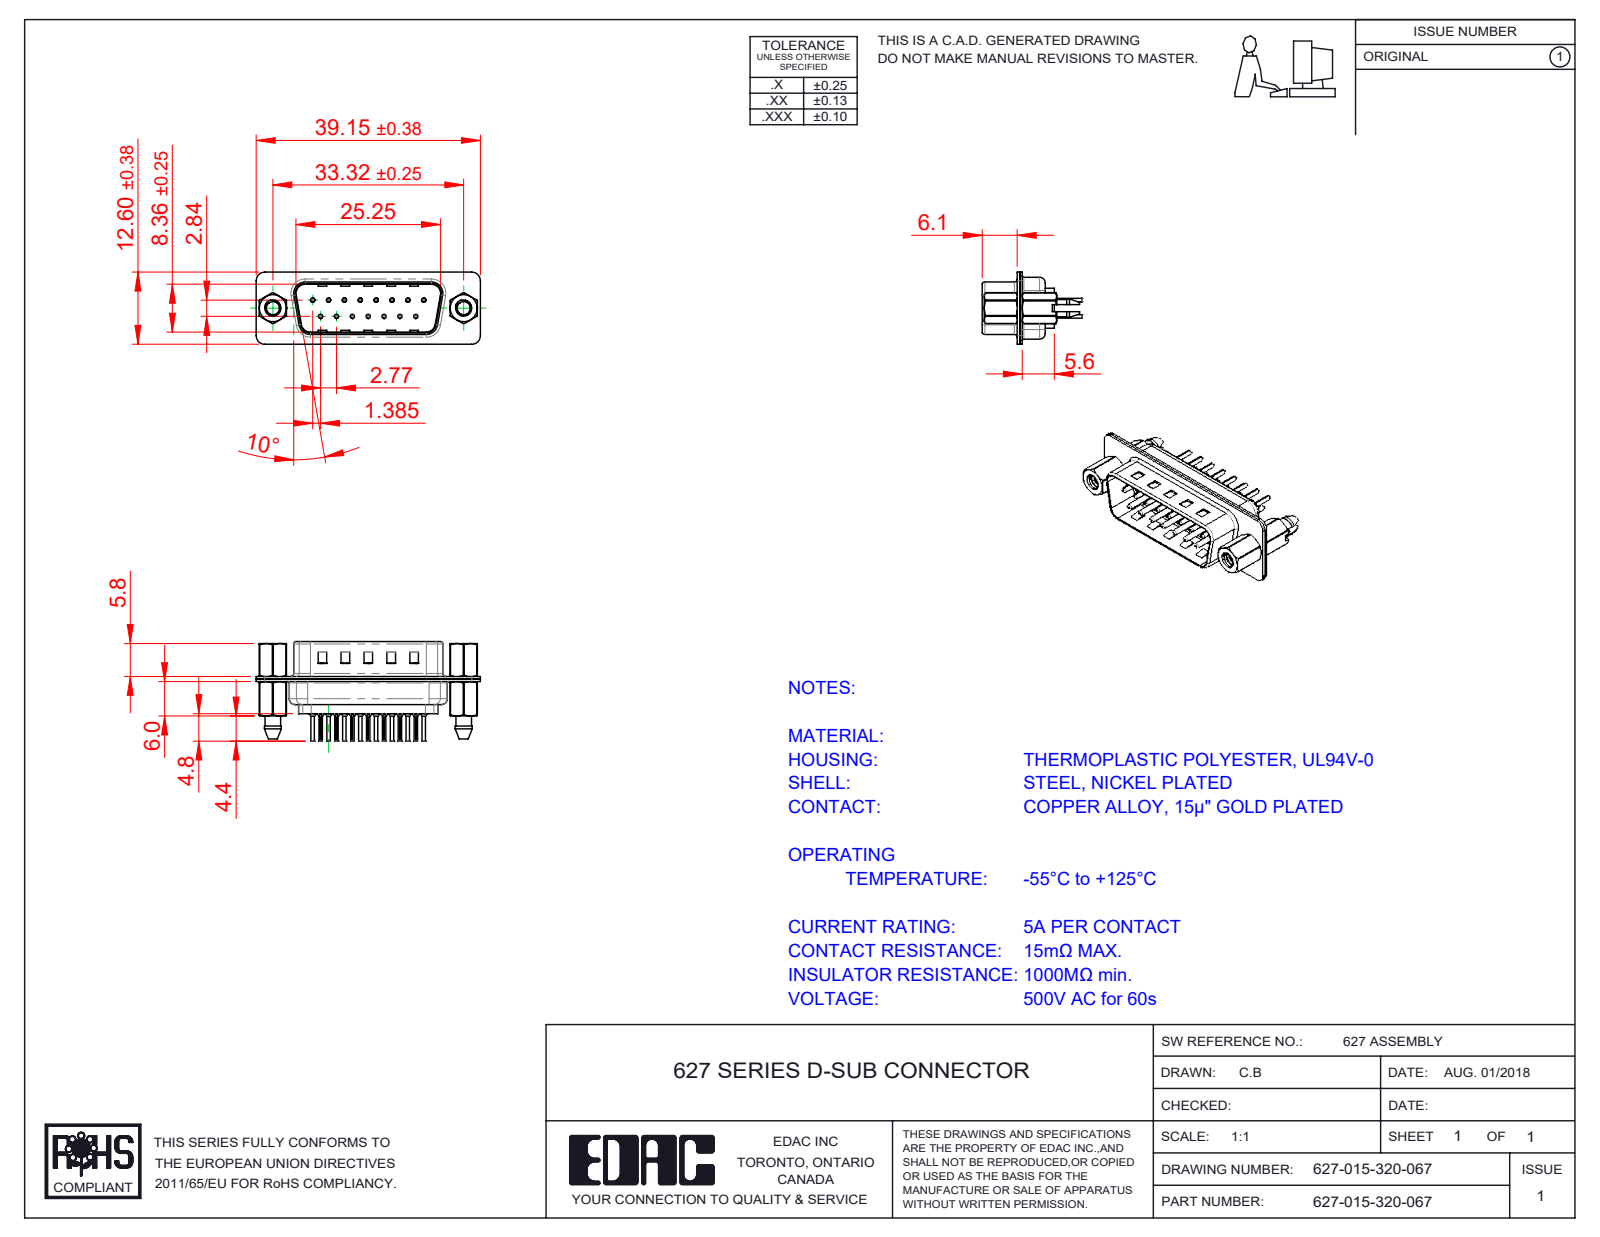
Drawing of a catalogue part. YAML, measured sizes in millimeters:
part_name: "627-015-320-067; 627 4-40 Hex Standoff; 627 Shell Front_15 Contacts; 627 Contact Row 1_20L (+4 more)"
step_written_by: "SolidWorks 2020 (CONFIG_CONTROL_DESIGN)"
units: millimeters
bodies: {solids: 22, faces: 2010, planar: 553, cylindrical: 792, other: 665}
overall_size: [39.15, 17.3, 12.6]
volume: 2158
surface_area: 6166
round_holes:
  - {diameter: 0.2, count: 15}
  - {diameter: 0.35, count: 15}
  - {diameter: 1.1, count: 15}
  - {diameter: 1.6, count: 15}
  - {diameter: 2.26, count: 2}
  - {diameter: 2.29, count: 2}
  - {diameter: 4, count: 2}
  - {diameter: 4.8, count: 2}
round_bosses_or_shafts:
  - {diameter: 2, count: 15}
  - {diameter: 1.5, count: 15}
  - {diameter: 0.75, count: 15}
  - {diameter: 0.6, count: 15}
  - {diameter: 4.9, count: 2}
  - {diameter: 2.79, count: 2}
partial_cylinders:
  - {radius: 0.1, count: 30}
  - {radius: 1.5, count: 18}
  - {radius: 2, count: 12}
  - {radius: 1.6, count: 10}
  - {radius: 0.5, count: 8}
  - {radius: 0.25, count: 4}
  - {radius: 0.6, count: 4}
  - {radius: 0.65, count: 4}
face_to_face_distances: [0.4, 0.45, 0.9, 0.82, 9.58, 8.76, 4.76, 1.5, 1.4, 6.5]
hole_center_spacings: [3.16, 2.77, 5.54, 8.31, 11.08, 5.03, 5.04, 7.48]
